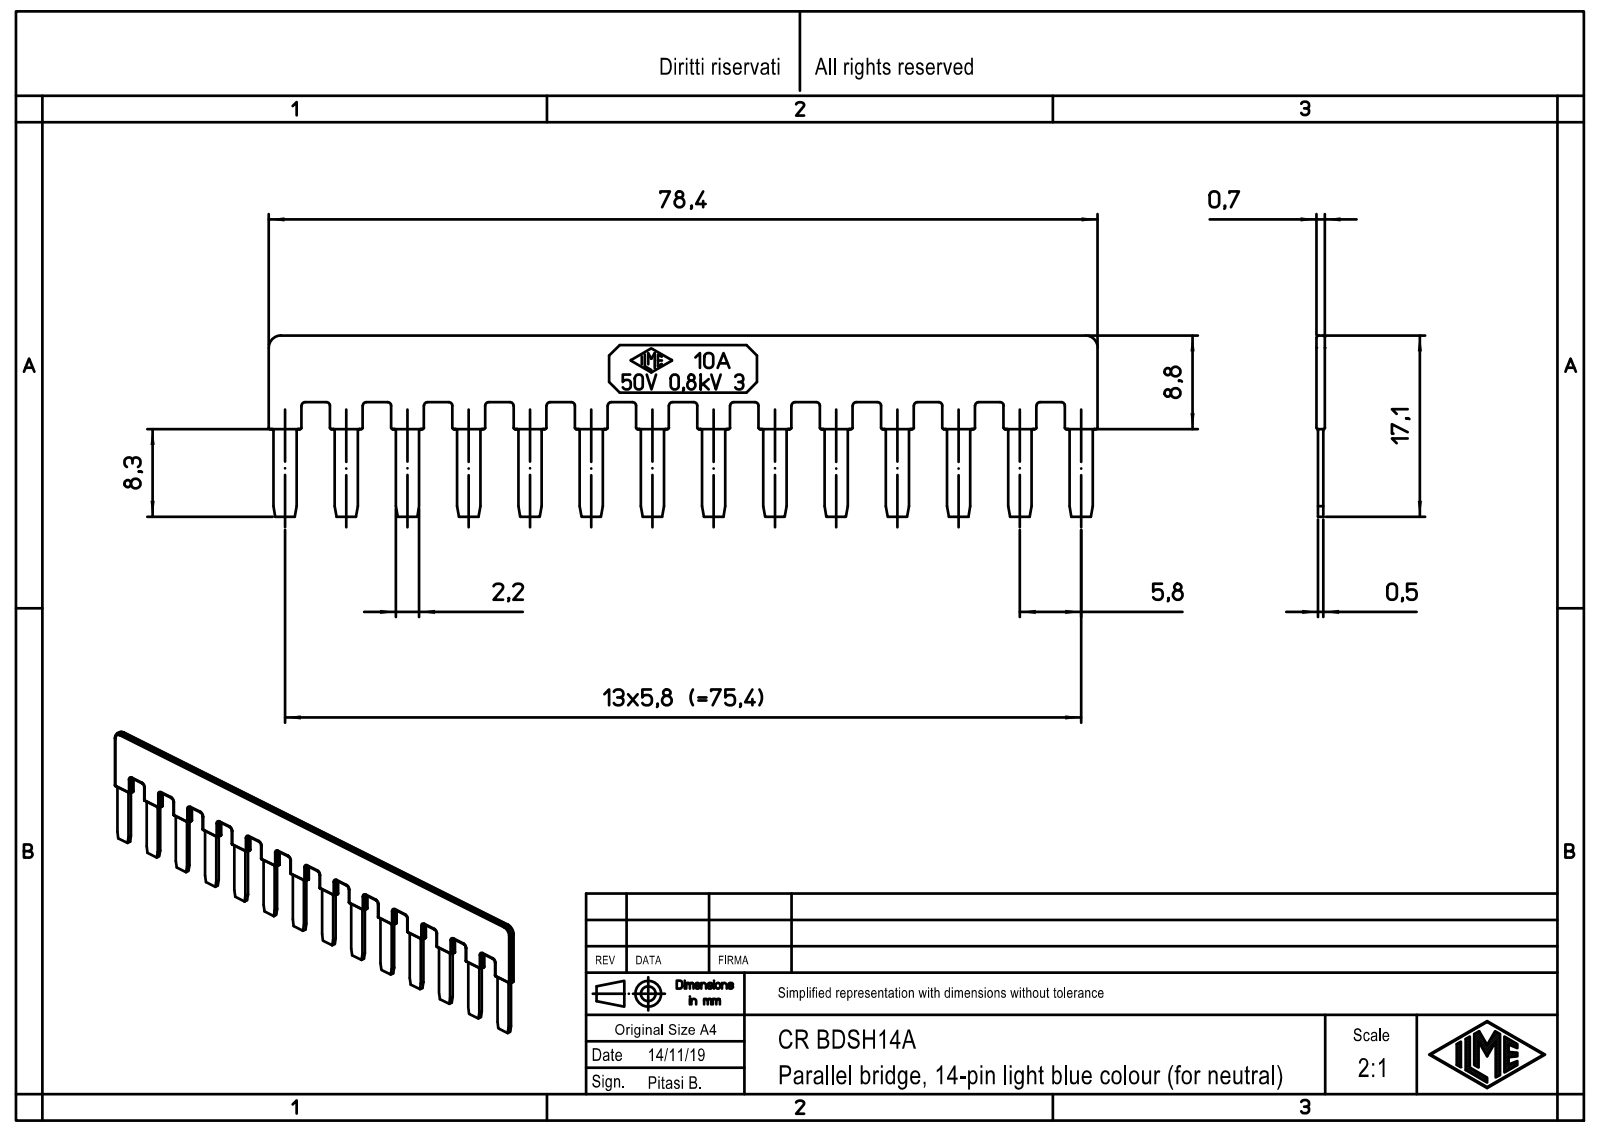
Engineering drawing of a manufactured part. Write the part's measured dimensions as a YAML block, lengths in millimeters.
part_name: "PONTE_14A"
step_written_by: "Creo Elements/Direct Modeling 20.1B 02-Apr-2019 (C) Parametric Technology GmbH (AUTOMOTIVE_DESIGN)"
units: millimeters
bodies: {solids: 1, faces: 470, planar: 162, cylindrical: 196, other: 112}
overall_size: [78.5, 17.15, 0.8]
volume: 607
surface_area: 1981
partial_cylinders:
  - {radius: 0.2, count: 60}
  - {radius: 0.1, count: 30}
  - {radius: 0.15, count: 28}
  - {radius: 0.35, count: 26}
  - {radius: 1.15, count: 2}
face_to_face_distances: [0.8, 0.65, 0.5, 5.8, 11.6, 17.4, 23.2, 2.2, 29, 3.6]
